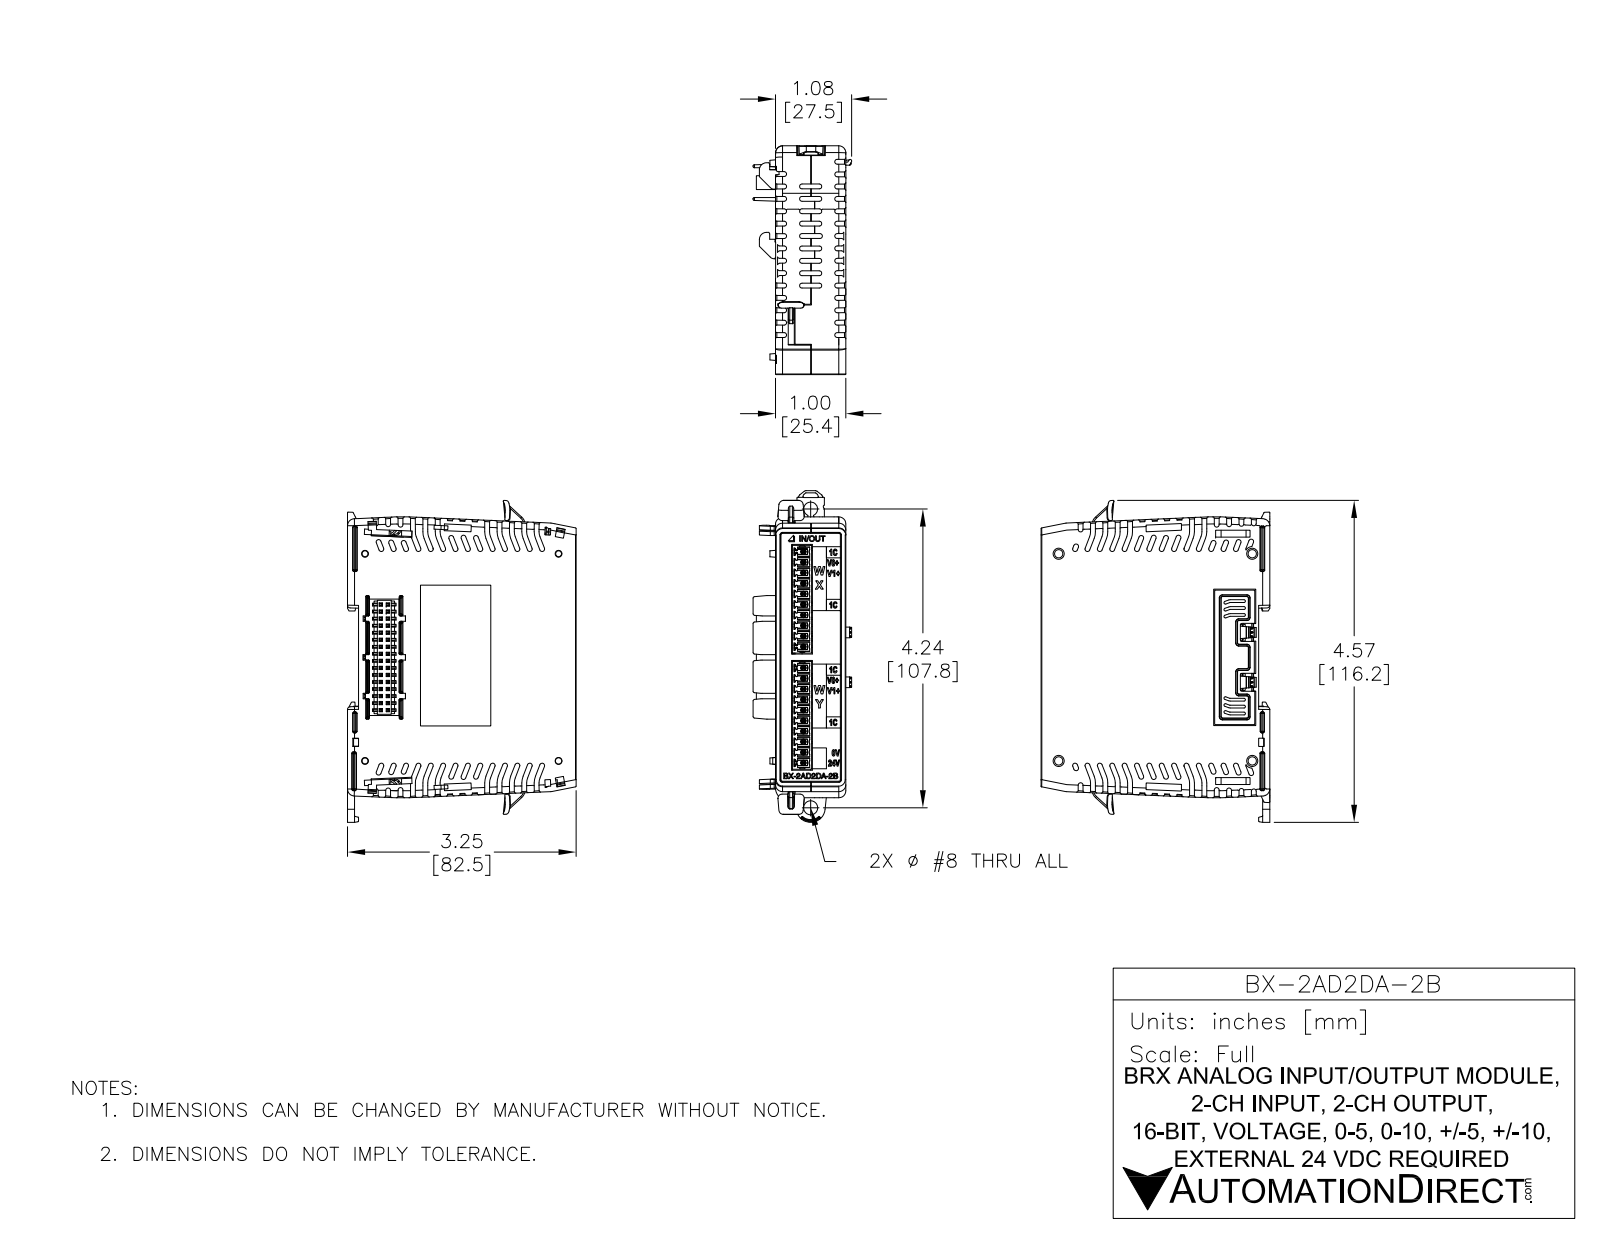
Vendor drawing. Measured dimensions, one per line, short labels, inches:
name: BX-2AD2DA-2B
written by: SolidWorks 2017 (AUTOMOTIVE_DESIGN)
unit: in
bodies: 11 solids, 4549 faces (3241 planar, 627 cylindrical, 681 other)
size: 4.586 × 3.25 × 1.401
volume: 9.457 in³; area: 89 in²
holes: 8× ⌀0.016, 2× ⌀0.016, 2× ⌀0.118, 2× ⌀0.118, 1× ⌀0.199
bosses: 2× ⌀0.111, 2× ⌀0.059, 1× ⌀0.071
rounds: 109× R0.02, 103× R0.008, 48× R0.005, 20× R0.062, 16× R0.012, 16× R0.014, 14× R0.01, 12× R0.008
face distances: 1, 0.835, 0.165, 3.053, 0.209, 0.627, 0.791, 3.063, 2.053, 1.01
hole spacings: 0.15, 0.3, 0.45, 0.6, 0.75, 1.651, 0.9, 1.501
